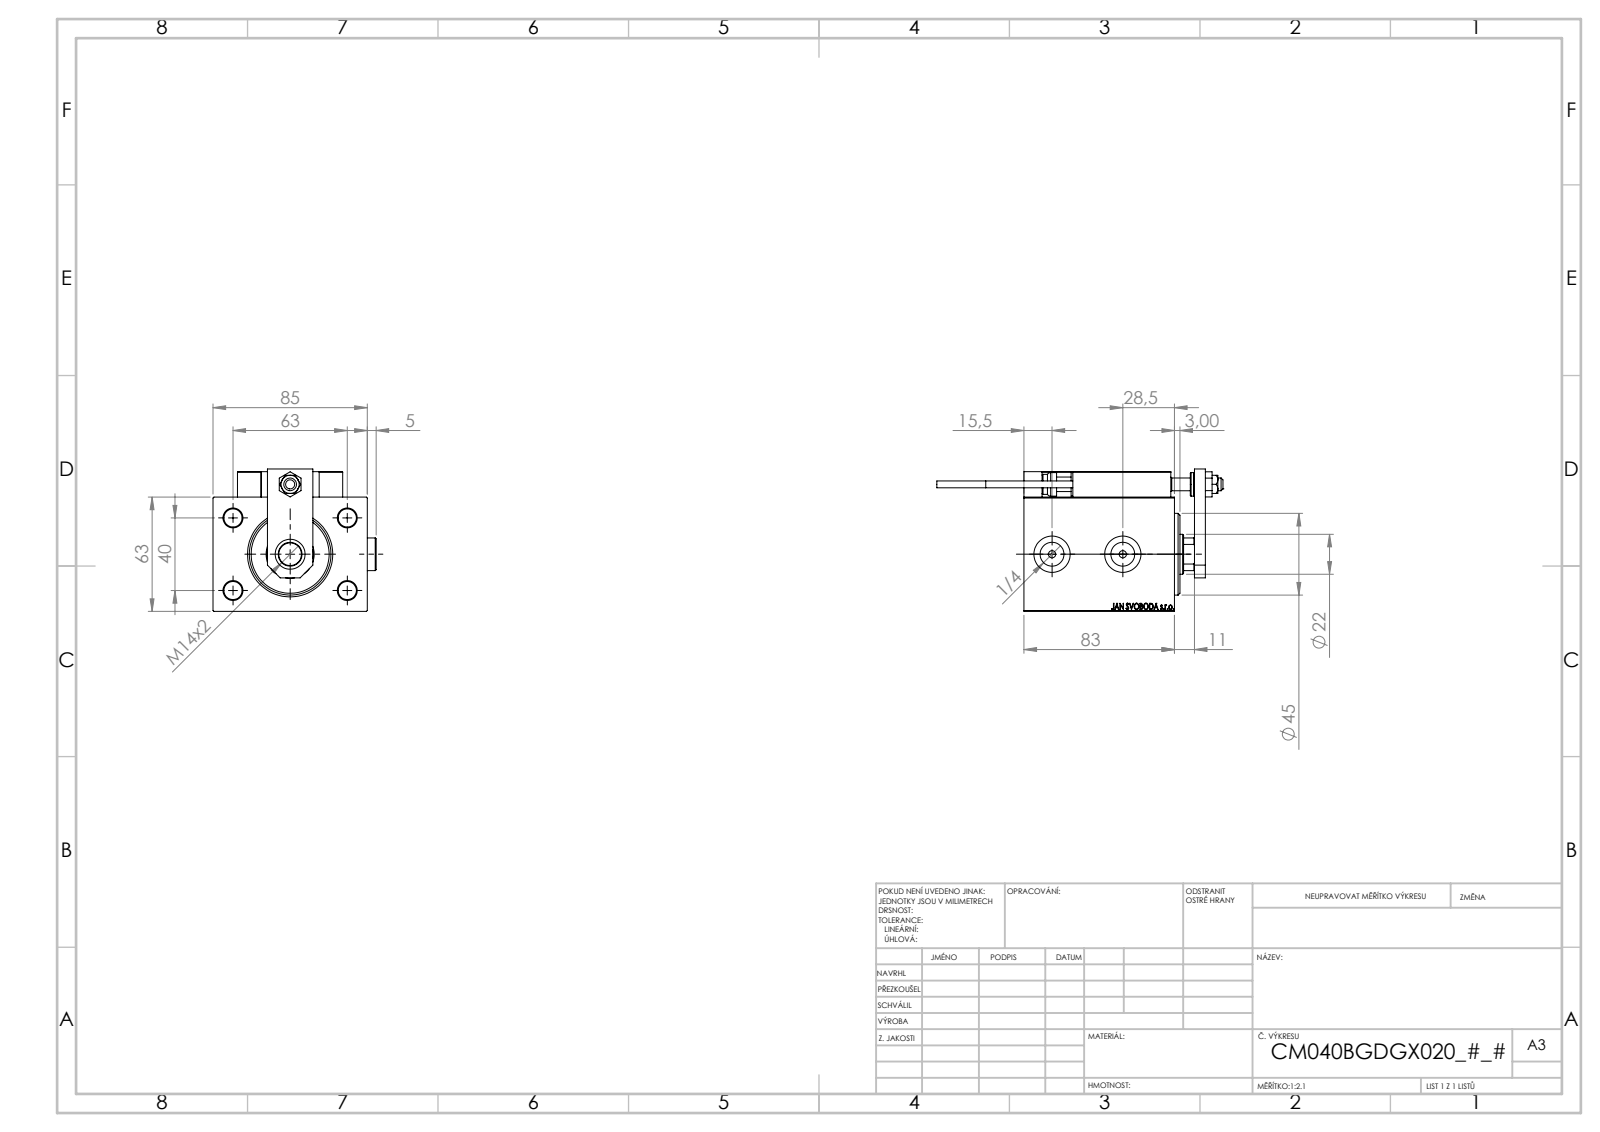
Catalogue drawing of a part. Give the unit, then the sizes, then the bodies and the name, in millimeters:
Units: millimetres
Overall size (bounding box): 157.7 × 89.9 × 78.5
Round holes (diameter × count): ⌀4 ×6, ⌀8 ×5, ⌀3.2 ×4, ⌀10 ×4, ⌀5 ×2, ⌀13.16 ×2, ⌀20 ×2, ⌀7 ×1, ⌀12.5 ×1, ⌀16.5 ×1, ⌀22 ×1, ⌀25.5 ×1
Round bosses / shafts (diameter × count): ⌀18 ×2, ⌀5 ×2, ⌀3.8 ×2, ⌀13 ×1, ⌀11 ×1
Partial cylindrical surfaces — rounded edges, fillets, slot ends (radius × count): R0.3 ×30, R3 ×2, R10.5 ×1
Main face-to-face distances: 63, 85, 32, 83, 14, 51, 10, 51.4, 77, 17
Hole centre spacings: 37.31, 11.37, 20, 29.59, 29.69, 35.06, 36.06, 36.53
Volume: 469 656 mm³ · Surface area: 92 421 mm²
Bodies: 26 solids, 1370 faces (595 planar, 198 cylindrical, 577 other)
Part name (STEP PRODUCT): SWITCH_X_FRONT_BACK; MAGNET; NUT_D12; V450CM_VC_B (+7 more)
STEP written by: SolidWorks 2019 (CONFIG_CONTROL_DESIGN)
